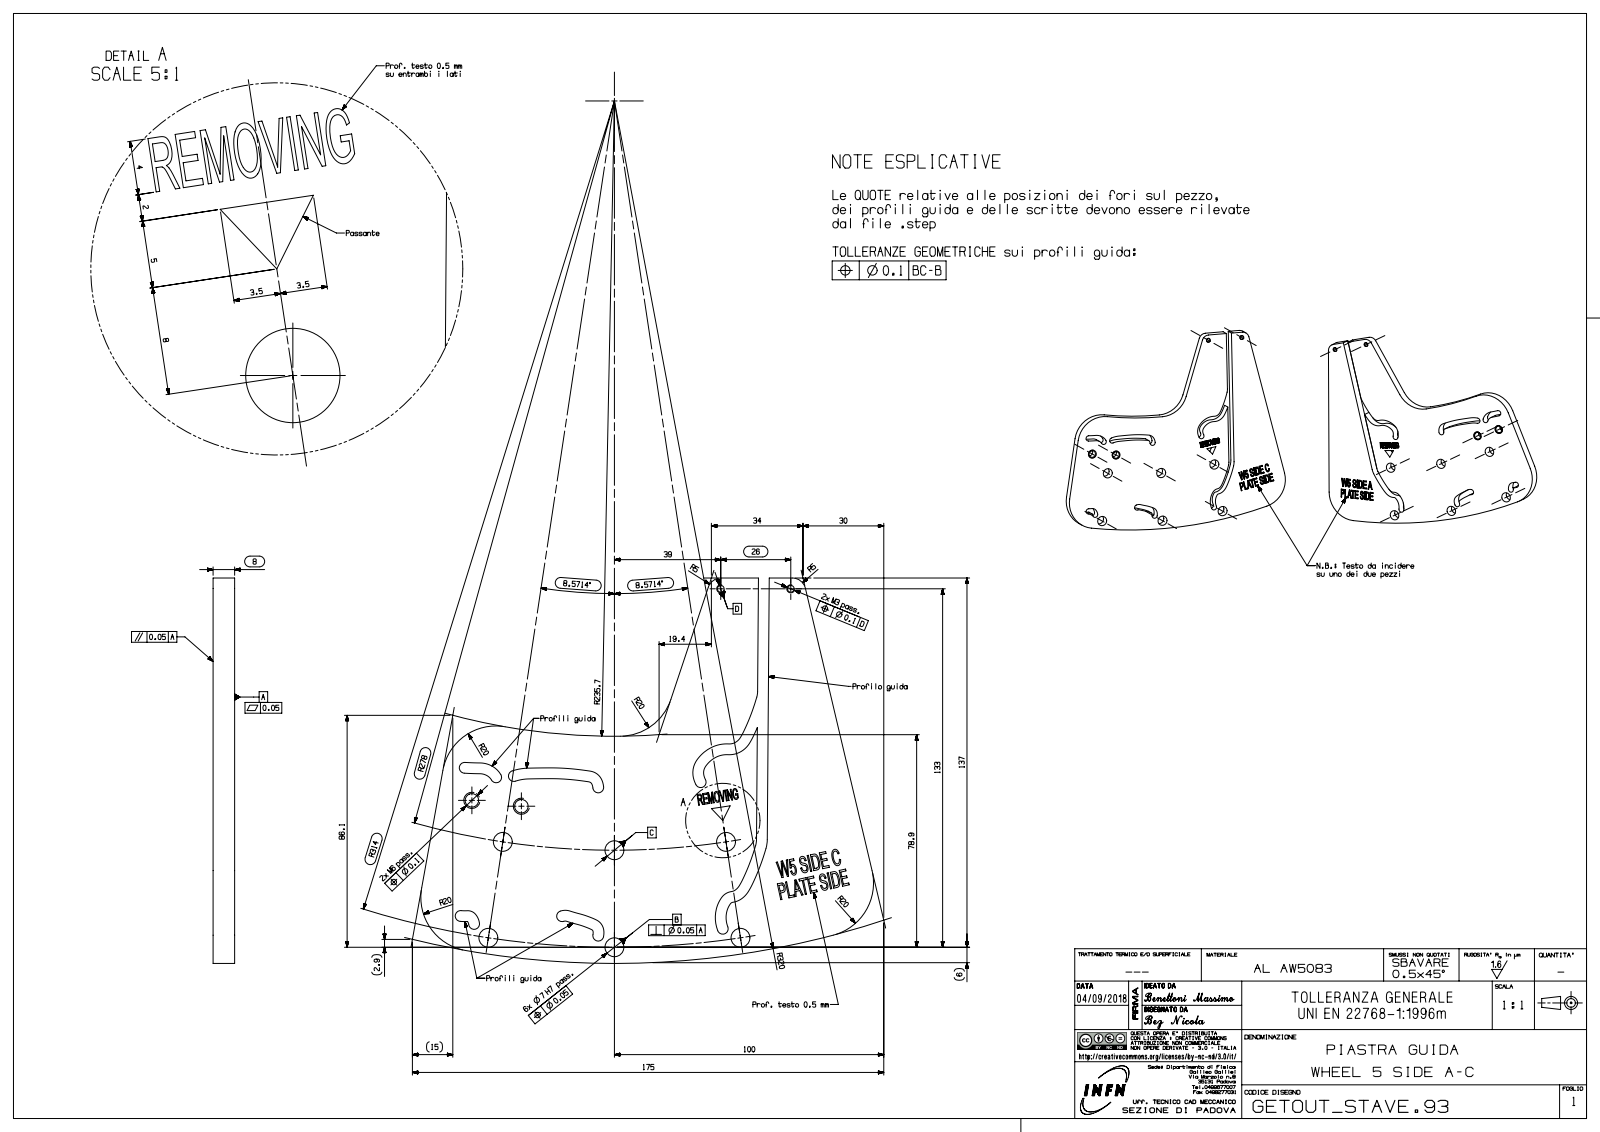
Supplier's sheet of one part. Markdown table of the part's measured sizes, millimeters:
| quantity | value |
| --- | --- |
| part name | bez8324385A6uy4 |
| STEP written by | SIEMENS PLM Software NX 12.0 (AUTOMOTIVE_DESIGN) |
| units | millimeters |
| bodies | 1 solid, 525 faces (385 planar, 31 cylindrical, 109 other) |
| overall size | 176.03 × 139.07 × 8 |
| volume | 116 042 mm³ |
| surface area | 39 685 mm² |
| round holes (diameter × count) | 7 × 6, 2.5 × 2, 5 × 2 |
| partial cylindrical surfaces (radius × count) | 2 × 10, 20 × 4, 5 × 2, 8 × 2, 12 × 1, 235.71 × 1, 320 × 1 |
| main face-to-face distances | 8, 3.98, 3.95, 0.5, 7.5, 7, 0.44, 0.71, 10.82, 5.3 |
| hole center spacings | 36, 41.55, 46.93, 56.97, 56.98, 14.91, 18.5, 19.2 |
